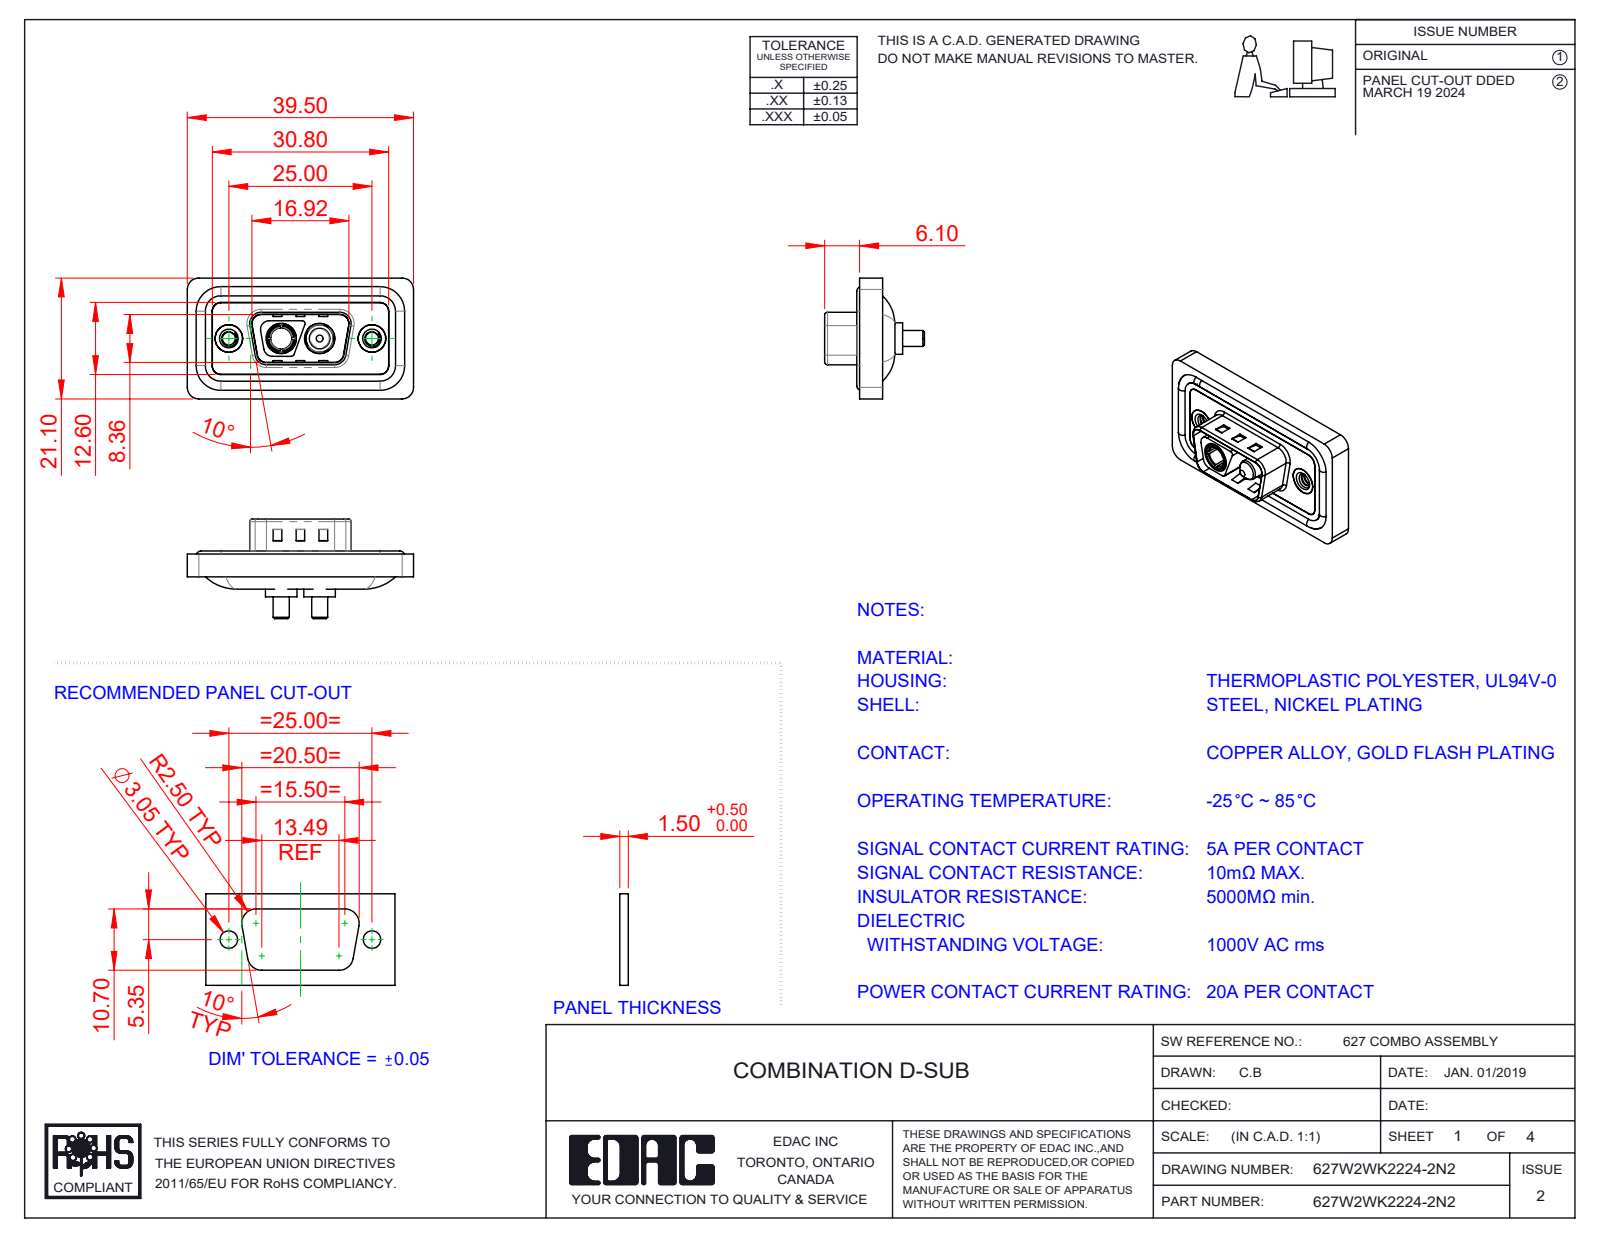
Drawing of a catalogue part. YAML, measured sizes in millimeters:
part_name: "Power Pin_20A S; 627W2WK2224-2N2; Power Socket_20A S; 627Combo Shell Rear_09 Contacts (+4 more)"
step_written_by: "SolidWorks 2023 (CONFIG_CONTROL_DESIGN)"
units: millimeters
bodies: {solids: 11, faces: 534, planar: 189, cylindrical: 227, other: 118}
overall_size: [39.5, 21.1, 17.4]
volume: 4554
surface_area: 7342
round_holes:
  - {diameter: 2.26, count: 2}
  - {diameter: 4, count: 2}
  - {diameter: 4.8, count: 2}
  - {diameter: 4.85, count: 2}
  - {diameter: 5, count: 2}
  - {diameter: 5.3, count: 2}
  - {diameter: 3.7, count: 1}
round_bosses_or_shafts:
  - {diameter: 1.6, count: 4}
  - {diameter: 5.5, count: 2}
  - {diameter: 5.2, count: 2}
  - {diameter: 4.9, count: 2}
  - {diameter: 4.75, count: 2}
  - {diameter: 3.75, count: 2}
  - {diameter: 2.8, count: 2}
  - {diameter: 4.96, count: 1}
partial_cylinders:
  - {radius: 1.5, count: 24}
  - {radius: 2, count: 18}
  - {radius: 0.5, count: 10}
  - {radius: 1.6, count: 8}
  - {radius: 0.25, count: 4}
  - {radius: 0.6, count: 4}
  - {radius: 0.65, count: 4}
  - {radius: 0.9, count: 4}
face_to_face_distances: [0.4, 1.1, 2.9, 0.5, 3.1, 1.6, 1.5, 4, 2.5, 1.8]
hole_center_spacings: [9.14, 15.86, 6.72, 25]
